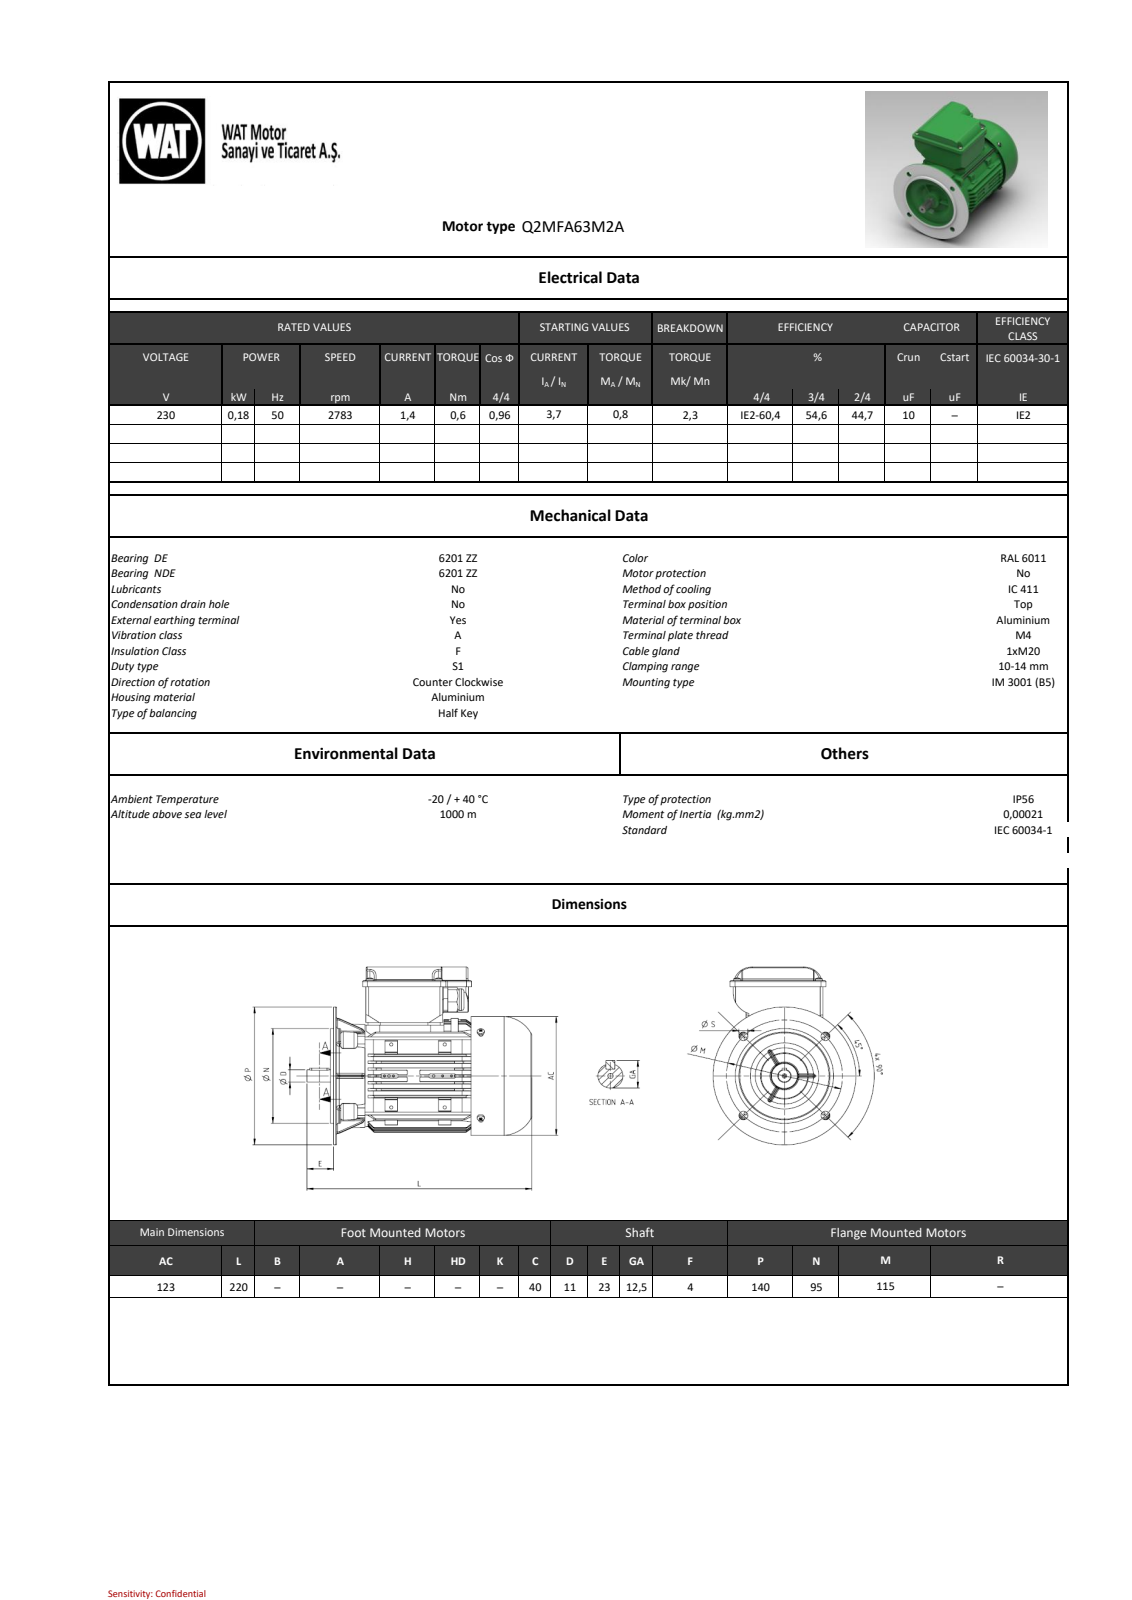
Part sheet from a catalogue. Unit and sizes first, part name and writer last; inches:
Units: inches
Overall size (bounding box): 8.641 × 7.425 × 5.52
Round holes (diameter × count): ⌀0.144 ×10, ⌀0.177 ×8, ⌀0.394 ×8, ⌀0.098 ×6, ⌀0.13 ×5, ⌀0.138 ×4, ⌀0.157 ×4, ⌀0.183 ×4, ⌀0.189 ×4, ⌀0.118 ×3, ⌀0.197 ×1, ⌀0.315 ×1
Round bosses / shafts (diameter × count): ⌀0.315 ×8, ⌀0.157 ×8, ⌀0.118 ×8, ⌀5.52 ×1, ⌀4.843 ×1, ⌀3.74 ×1, ⌀2.756 ×1, ⌀1.181 ×1
Partial cylindrical surfaces — rounded edges, fillets, slot ends (radius × count): R0.02 ×210, R0.039 ×82, R0.079 ×66, R0.098 ×20, R0.197 ×11, R0.118 ×9, R0.217 ×9, R0.059 ×8
Main face-to-face distances: 0.118, 0.039, 0.098, 0.276, 1.101, 0.177, 0.276, 0.059, 0.984, 0.157
Hole centre spacings: 1.69, 4.072, 2.165, 1.733, 2.264, 3.118, 3.202, 2.144
Volume: 37.61 in³ · Surface area: 643.2 in²
Bodies: 34 solids, 2176 faces (1142 planar, 733 cylindrical, 301 other)
Part name (STEP PRODUCT): BY6434017xx_004-TK_QM63-80; BY6424130xx_004-TKK_QM63-80; BY6434010xx_005-MOTOR_KAPAGI_QS63_FA_ISLEME; BY6423003xx_006-FAN_KAPAGI_QS63 (+7 more)
STEP written by: SIEMENS PLM Software NX2206.8101 (AUTOMOTIVE_DESIGN)
